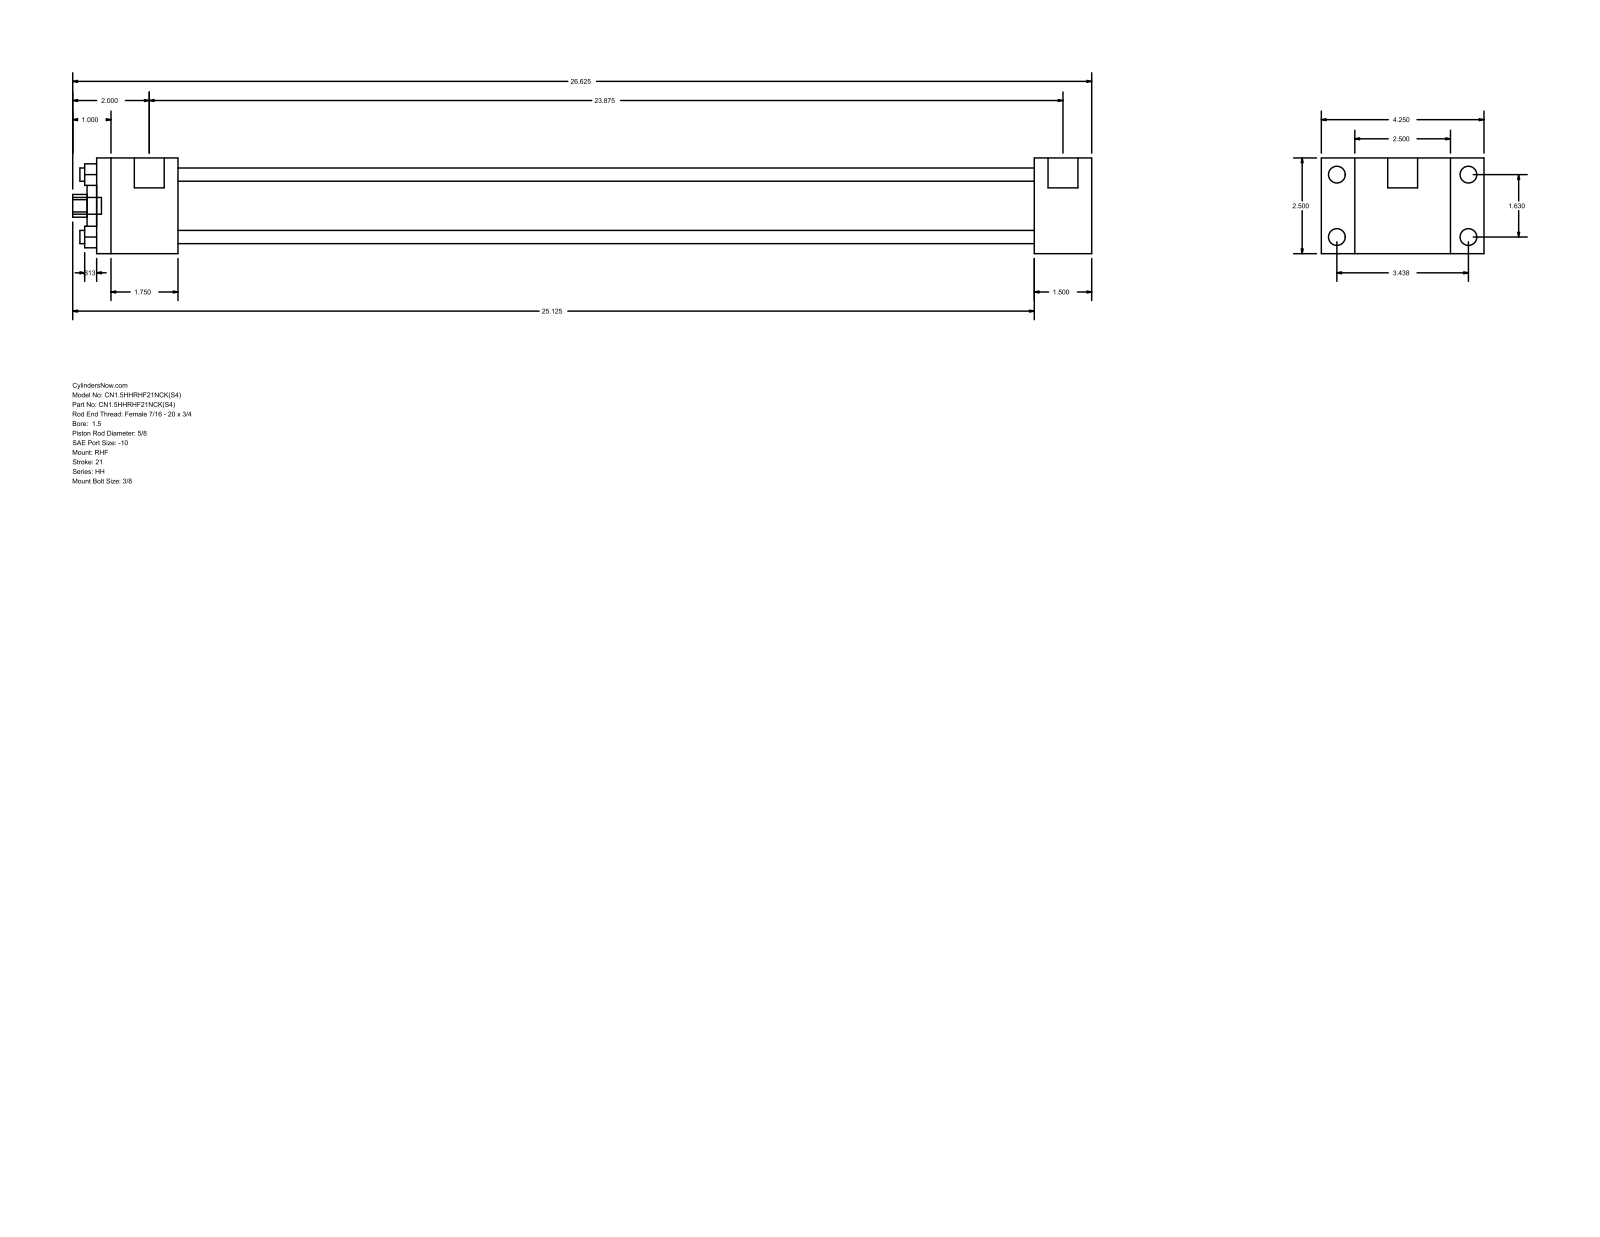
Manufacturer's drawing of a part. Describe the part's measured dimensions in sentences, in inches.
The part is named "HH_RHF__0150_0.625". Its 3-D file was written by "GSSL Pune (CONFIG_CONTROL_DESIGN)". It is 0 solids with 88 faces: 60 planar, 28 cylindrical and 0 other. Overall it measures 26.625 by 4.25 by 2.5 inches. Round holes: 4 of diameter 0.345, 1 of diameter 0.625, 1 of diameter 1.125, 1 of diameter 1.75. Round bosses or shafts: 4 of diameter 0.438, 4 of diameter 0.219, 2 of diameter 0.781, 1 of diameter 0.437. Partial cylindrical surfaces (rounded edges, fillets, slot ends): 1 of radius 0.297. The main face-to-face distances are 2.5, 1.5, 0.875, 3.375, 24.5, 26, 4.25, 2.125, 22.375, 23.875. The hole center spacings are 1.152, 1.63, 2.305.
